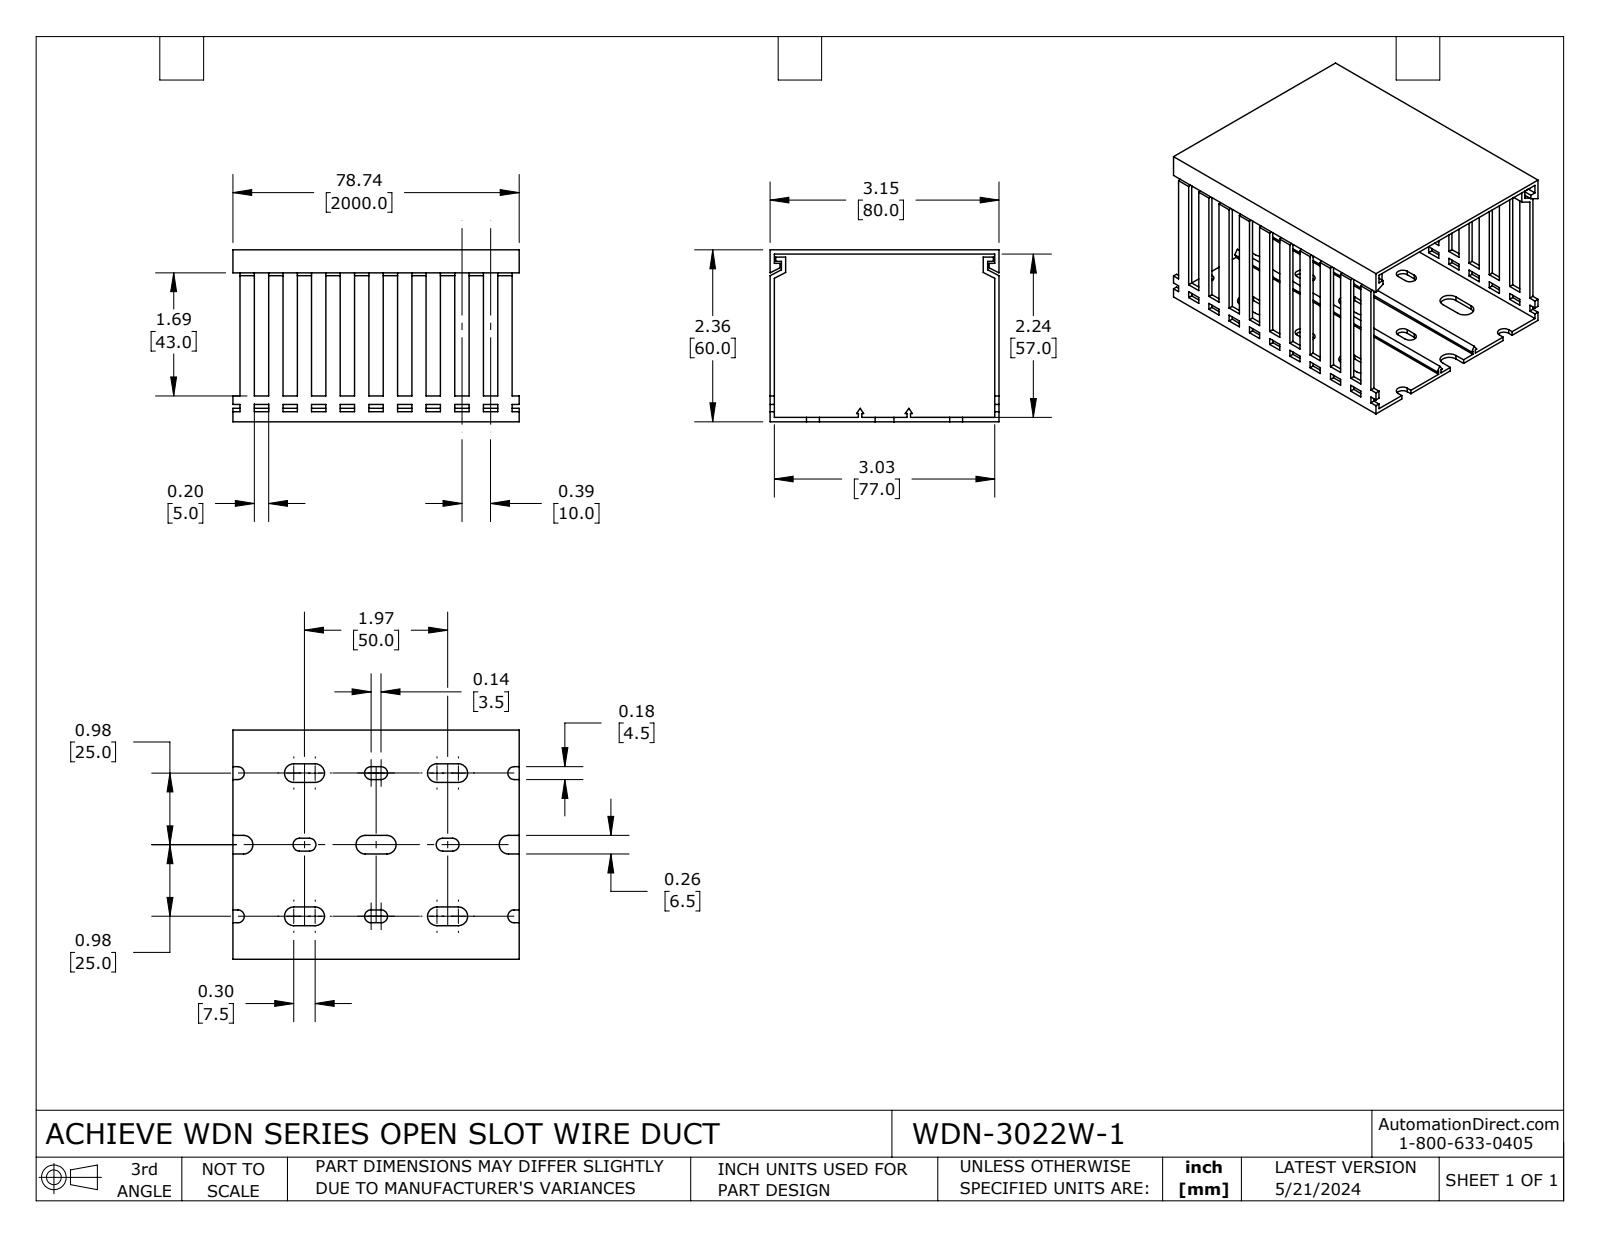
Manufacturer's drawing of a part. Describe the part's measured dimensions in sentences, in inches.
The part is named "WDN-3022W-1". Its 3-D file was written by "SolidWorks 2023 (CONFIG_CONTROL_DESIGN)". It is 2 solids with 398 faces: 362 planar, 36 cylindrical and 0 other. Overall it measures 3.937 by 3.15 by 2.362 inches. Its volume is 2.209 cubic inches and its surface area 83.02 square inches. Partial cylindrical surfaces (rounded edges, fillets, slot ends): 12 of radius 0.089, 12 of radius 0.128. The main face-to-face distances are 0.059, 2.303, 2.362, 2.244, 3.091, 3.15, 3.031, 0.394, 0.197, 0.591.
